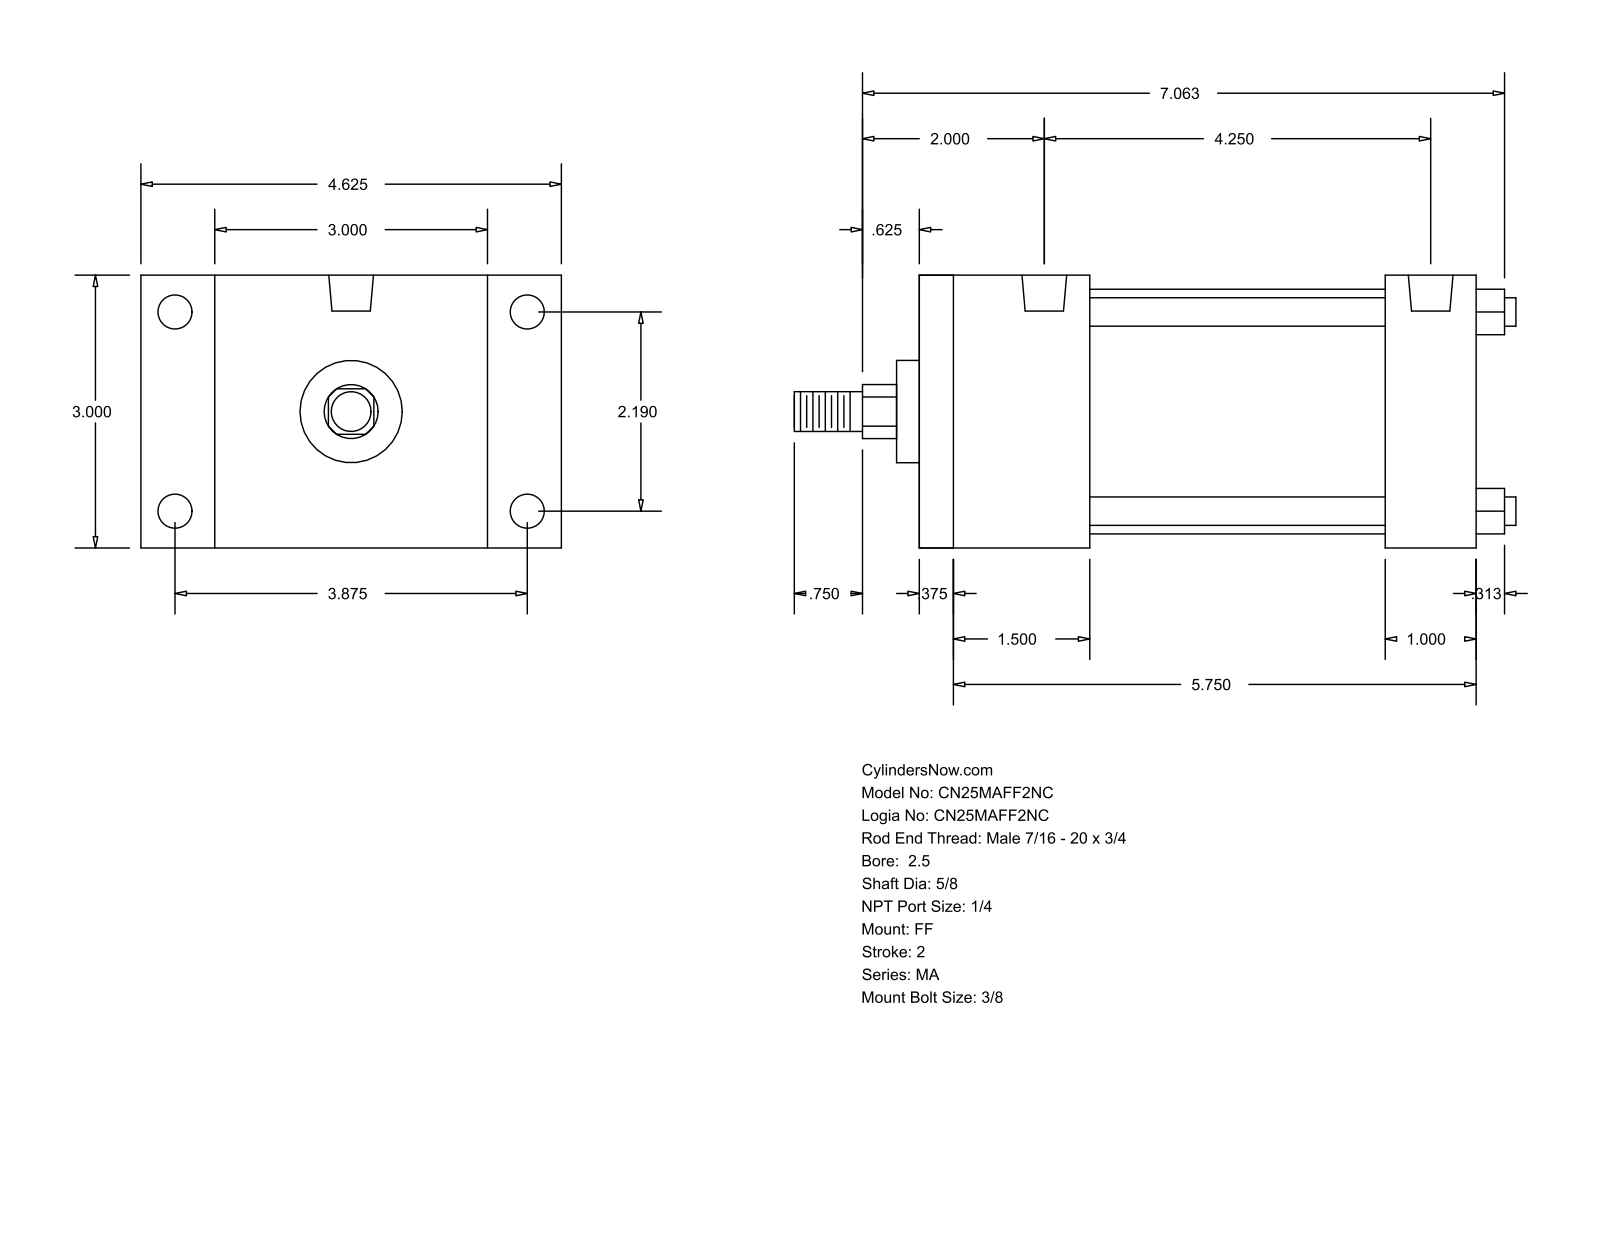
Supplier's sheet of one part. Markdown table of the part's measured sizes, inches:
| quantity | value |
| --- | --- |
| part name | MA_FF__0250_0.625 |
| STEP written by | GSSL Pune (CONFIG_CONTROL_DESIGN) |
| units | inches |
| bodies | 0 solids, 92 faces (64 planar, 28 cylindrical, 0 other) |
| overall size | 7.937 × 4.625 × 3 |
| round holes (diameter × count) | 0.313 × 4, 0.375 × 4, 0.492 × 2 |
| round bosses / shafts (diameter × count) | 0.313 × 4, 2.69 × 1, 1.125 × 1, 0.625 × 1, 0.437 × 1 |
| partial cylindrical surfaces (radius × count) | 0.297 × 1 |
| main face-to-face distances | 3, 6.125, 5.75, 0.375, 1, 3.25, 1.875, 5.125, 1.5, 4.75 |
| hole center spacings | 2.19, 3.875, 4.25, 4.451 |
